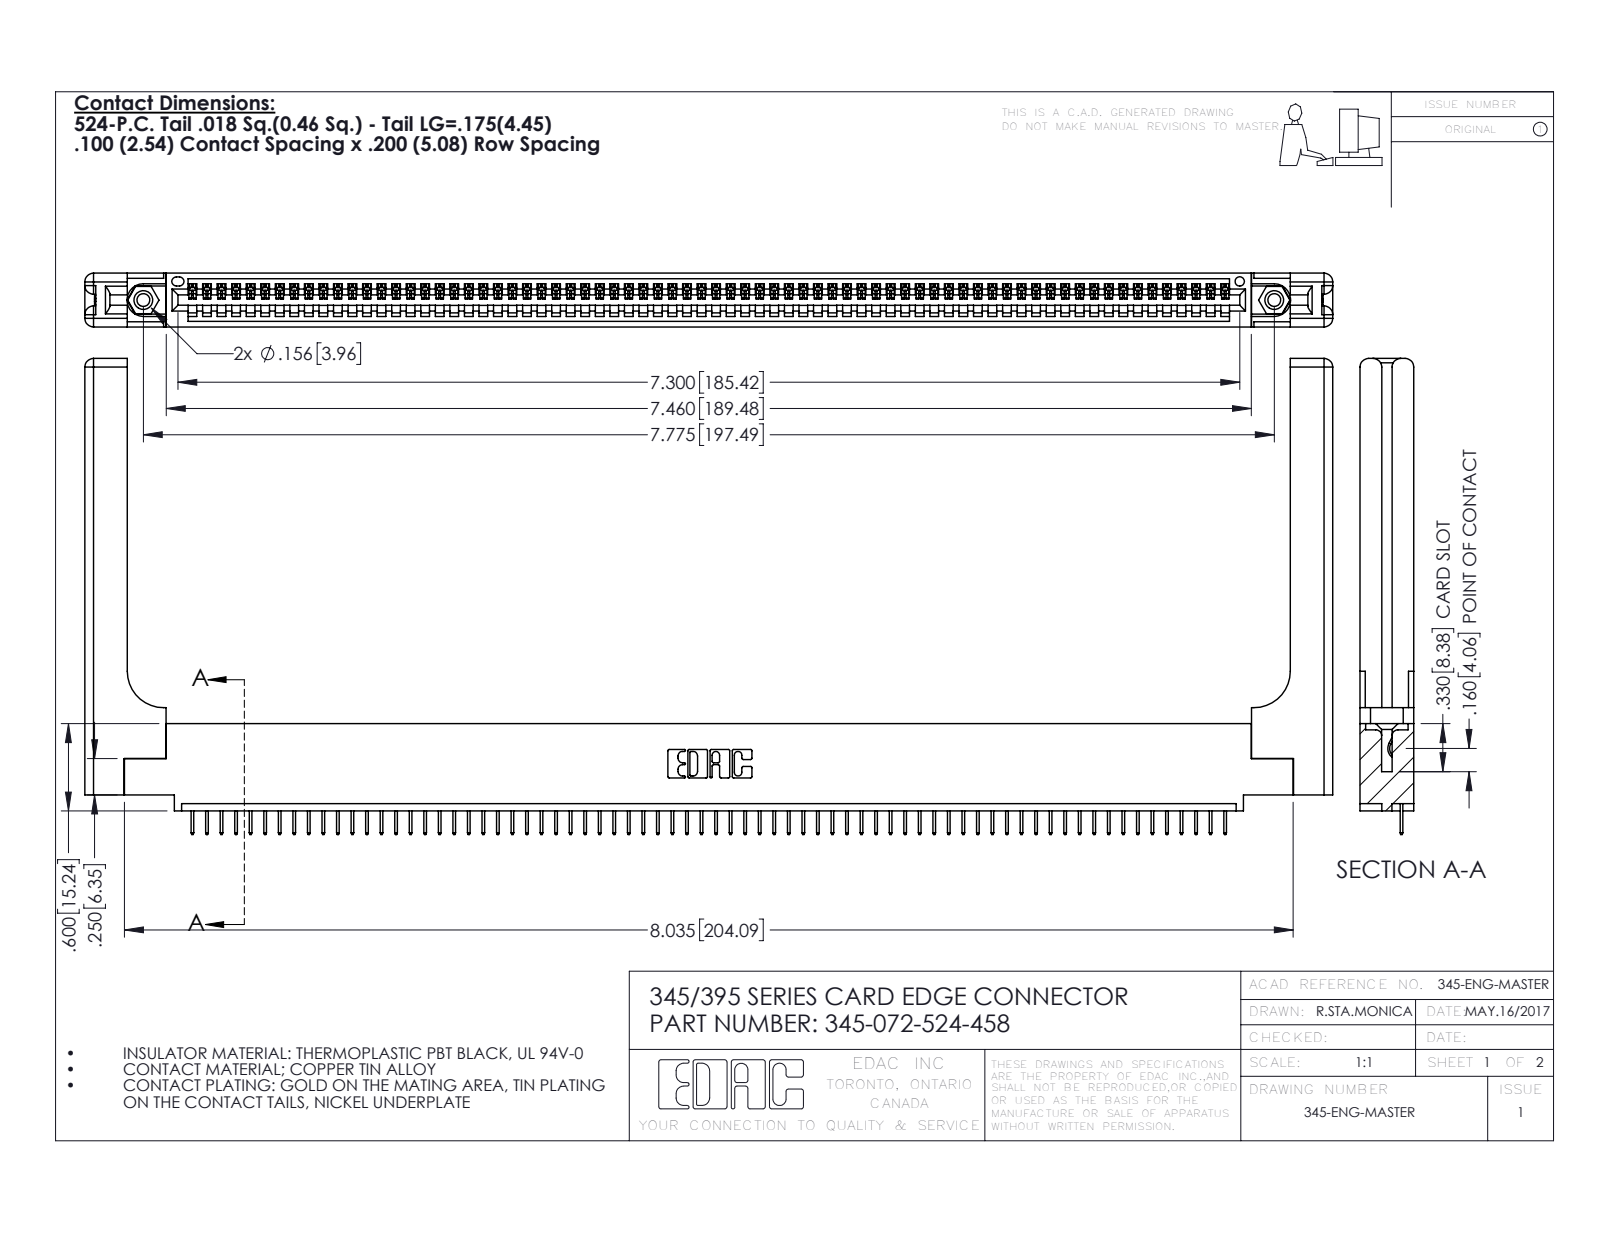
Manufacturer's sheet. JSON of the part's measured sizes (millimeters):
{"part_name": "345-292-001_345-293-124; 345-250-001_345-250-001-102; 345 Part_0.110 Offset - 0.156 Dia-TH; 345-072-524-458 (+1 more)", "step_written_by": "SolidWorks 2016 (CONFIG_CONTROL_DESIGN)", "units": "millimeters", "bodies": {"solids": 77, "faces": 4850, "planar": 3544, "cylindrical": 1246, "other": 60}, "overall_size": [217.9, 83.1, 9.4], "volume_mm3": 29090, "surface_area_mm2": 32240, "round_holes": [[2.3, 2], [3.2, 2], [4, 2], [1.6, 1]], "round_bosses_or_shafts": [[3.9, 2]], "partial_cylinders_radius": [[0.2, 144], [0.3, 22], [1.5, 16], [0.2, 6], [0.8, 6], [0.7, 3], [0.8, 2], [0.8, 2]], "face_to_face_distances": [1.8, 9.4, 7.6, 2.5, 6.9, 0.6, 5.1, 5.7, 3.8, 3.8], "hole_center_spacings": [6.9, 191.5, 197.5]}
